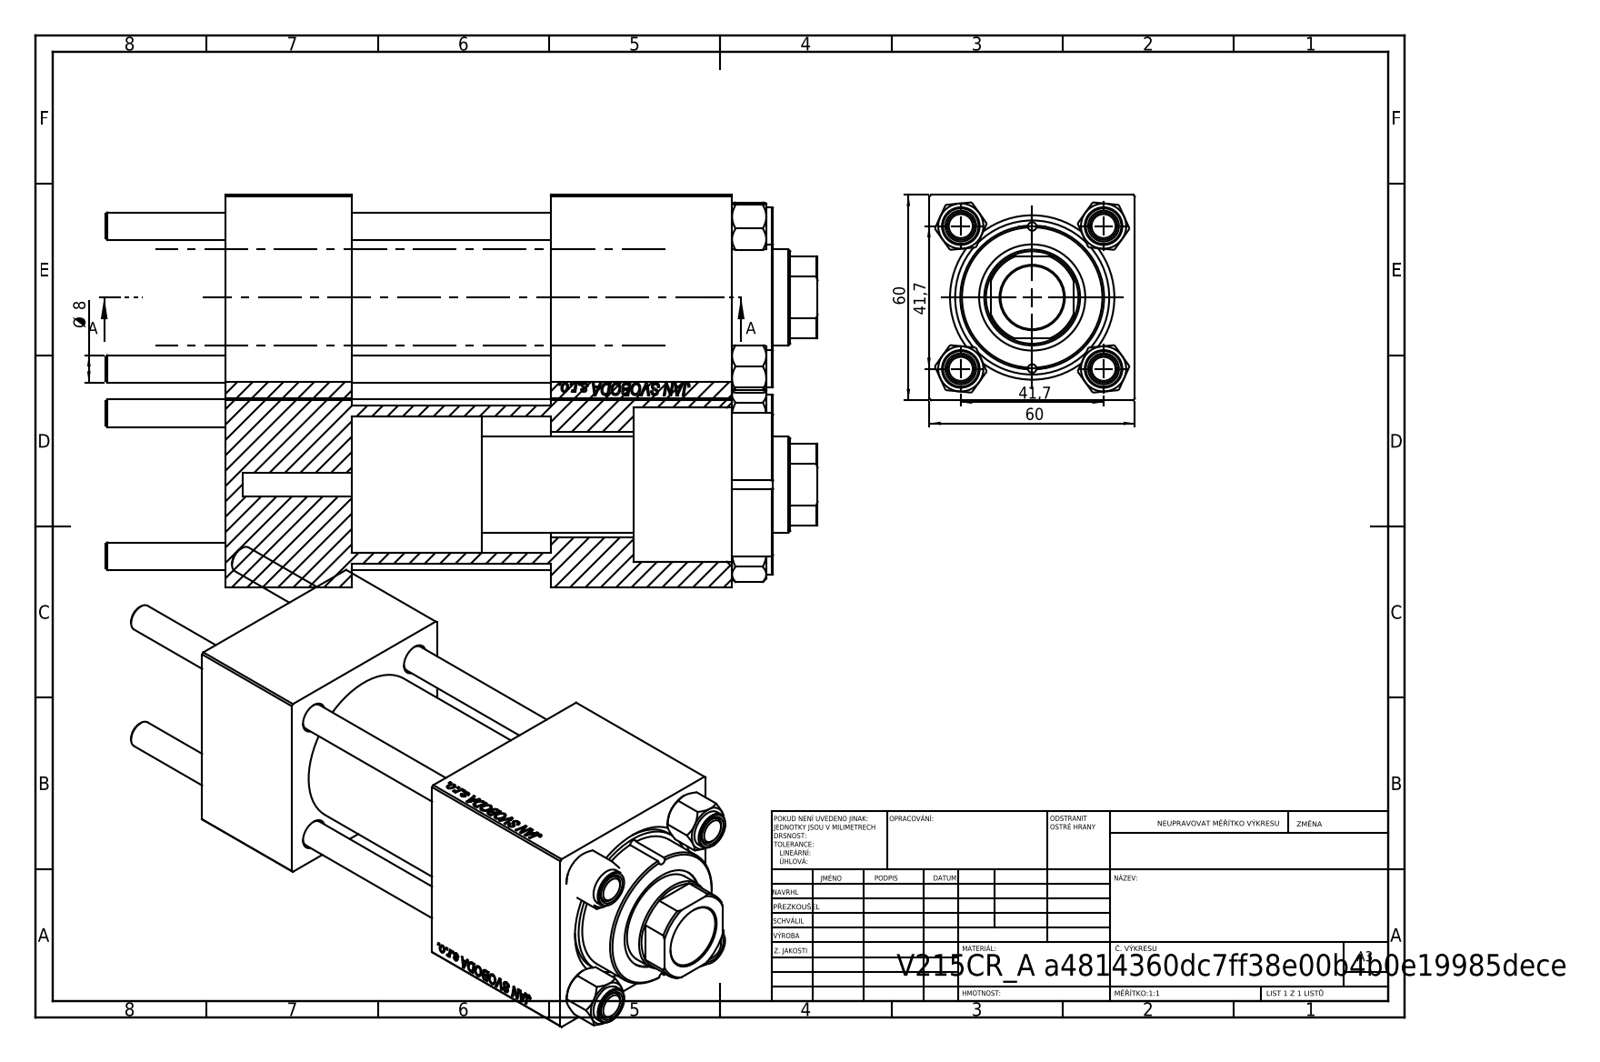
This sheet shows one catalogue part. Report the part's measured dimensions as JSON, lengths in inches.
{"part_name": "V215CR_BODY_A; CR025_012_A_0_G_A_G_M_020_+#_##_TYCINKA; V215CR_VCP; V215_VC_A (+1 more)", "step_written_by": "SolidWorks 2019 (CONFIG_CONTROL_DESIGN)", "units": "inches", "bodies": {"solids": 11, "faces": 1141, "planar": 523, "cylindrical": 82, "other": 536}, "overall_size": [8.189, 2.362, 2.362], "volume_in3": 26.57, "surface_area_in2": 186.4, "round_holes": [[0.315, 4], [0.098, 2], [0.276, 2], [0.656, 2], [0.945, 2], [0.728, 1], [1.102, 1], [1.22, 1], [1.575, 1], [1.772, 1]], "round_bosses_or_shafts": [[0.433, 4], [1.811, 1], [1.654, 1]], "partial_cylinders_radius": [[0.531, 1]], "face_to_face_distances": [2.362, 1.457, 2.283, 3.74, 2.087, 5.827, 4.37, 4.697, 3.24, 0.957], "hole_center_spacings": [0.821, 1.161, 1.642, 1.832, 0.817, 2.322, 1.634, 3.642]}
